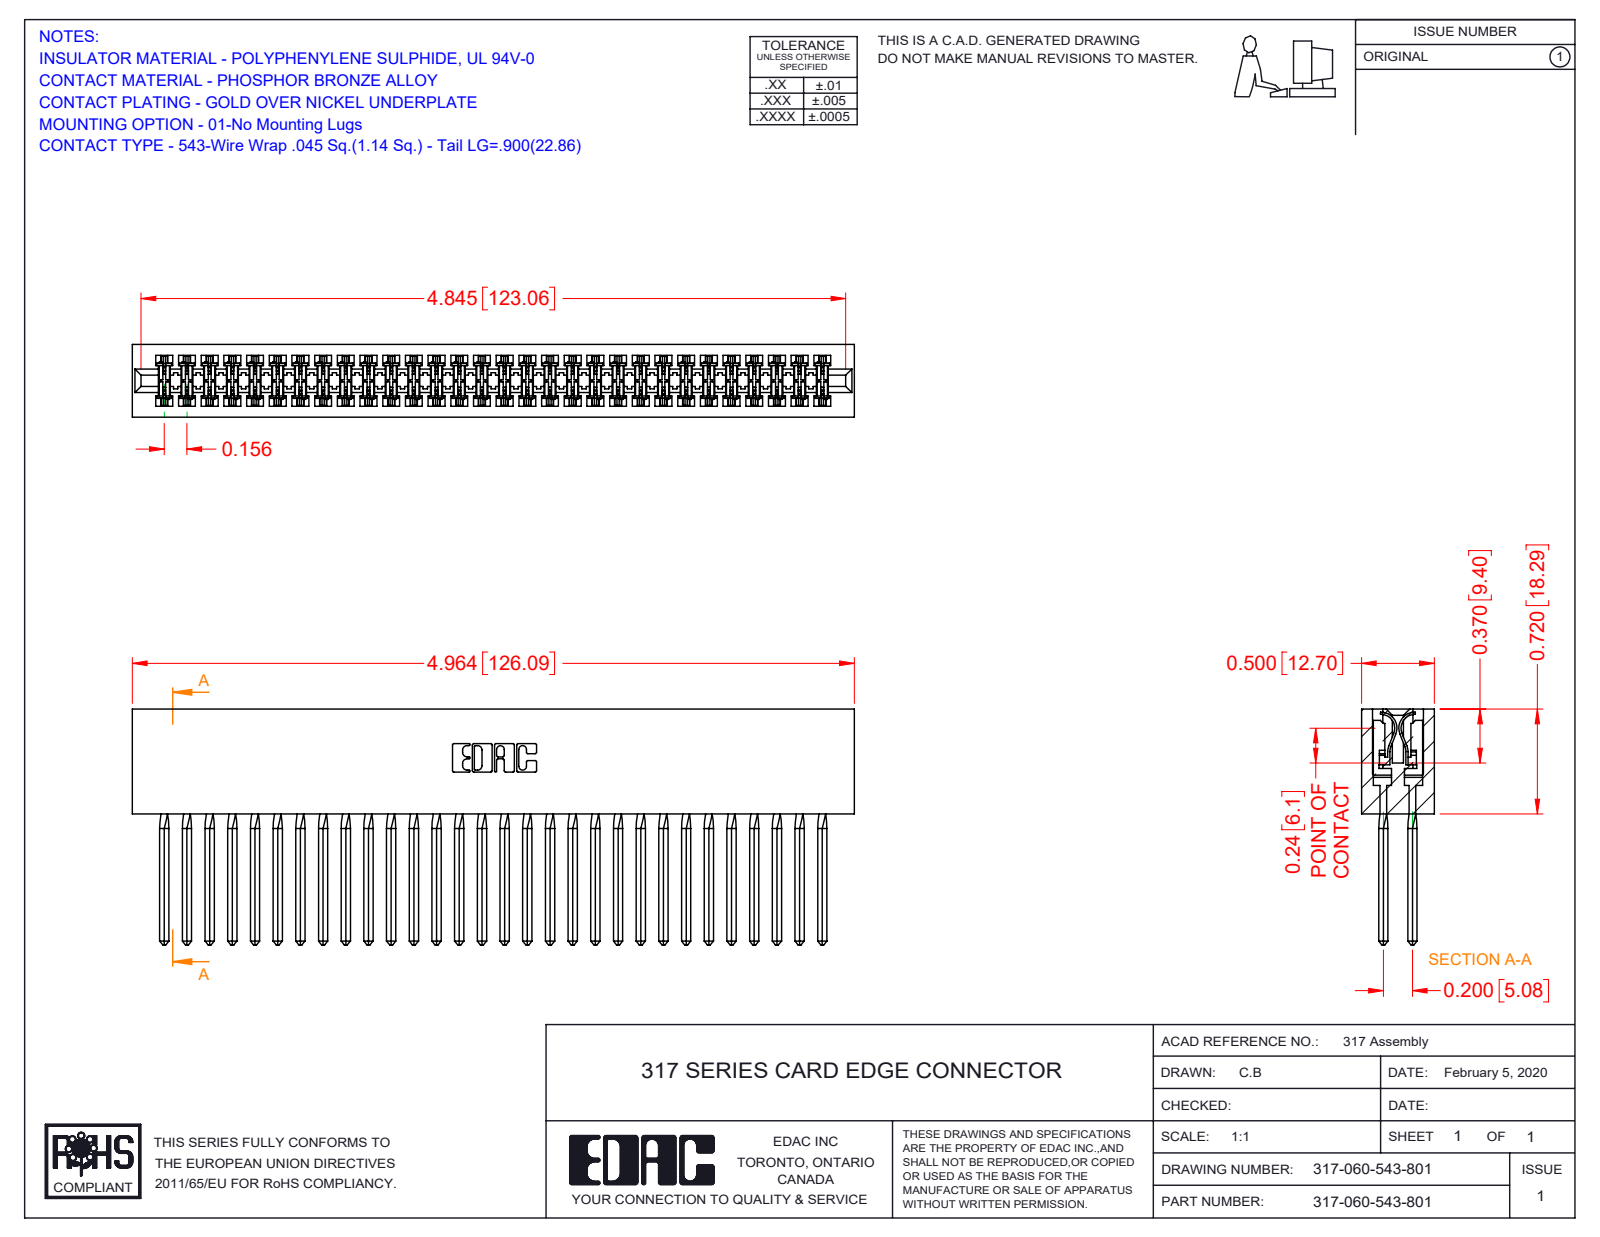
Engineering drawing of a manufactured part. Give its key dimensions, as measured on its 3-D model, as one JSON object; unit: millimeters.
{"part_name": "317 Part_Lugless; 317-060-543-801; 317-290-001_543", "step_written_by": "SolidWorks 2016 (CONFIG_CONTROL_DESIGN)", "units": "millimeters", "bodies": {"solids": 61, "faces": 5430, "planar": 4430, "cylindrical": 760, "other": 240}, "overall_size": [126.1, 41.1, 12.7], "volume_mm3": 22840, "surface_area_mm2": 34460, "partial_cylinders_radius": [[0.4, 120], [0.3, 22], [0.2, 6], [0.8, 6], [0.7, 3], [2.4, 2], [2.5, 2], [2.8, 2]], "face_to_face_distances": [1.9, 12.7, 10.8, 8.9, 2.8, 5, 2.4, 5.1, 18.3, 2.9]}
